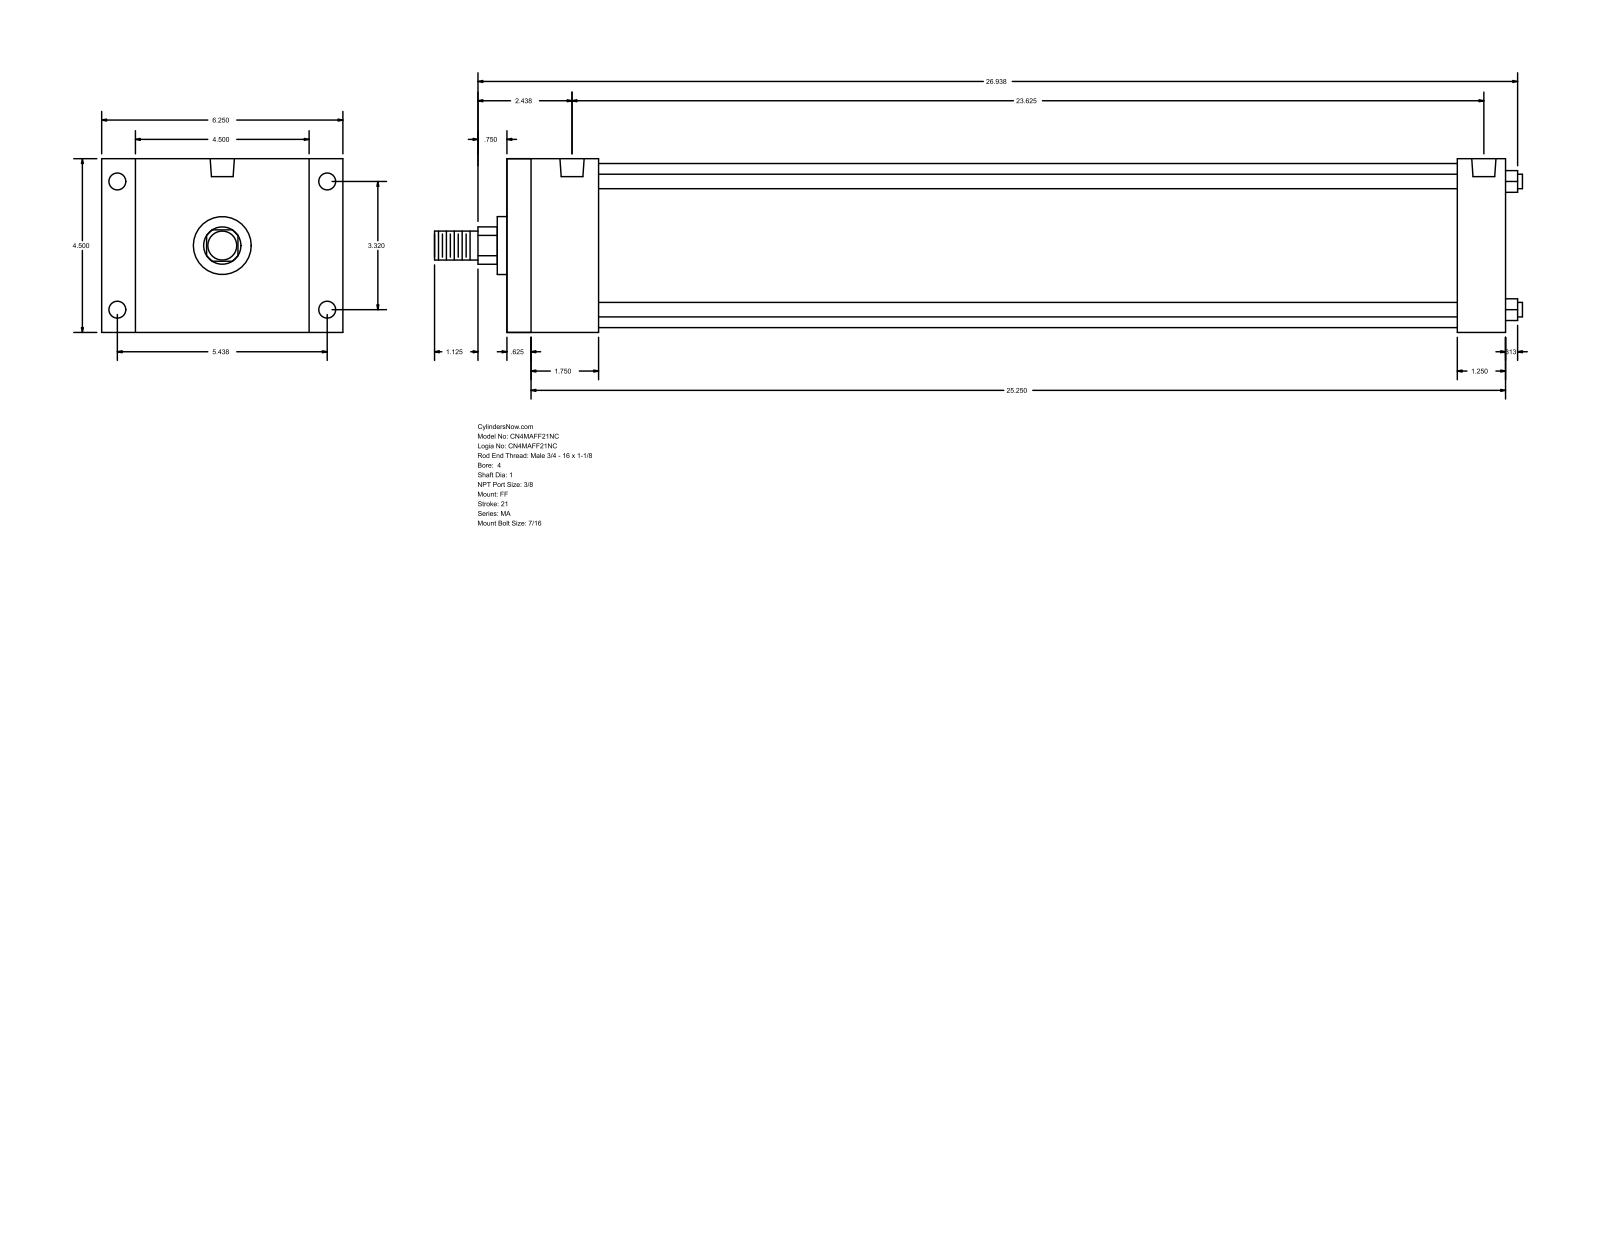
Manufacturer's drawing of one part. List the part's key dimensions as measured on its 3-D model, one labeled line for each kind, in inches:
Part name (STEP PRODUCT): MA_FF__0400_1
STEP written by: GSSL Pune (CONFIG_CONTROL_DESIGN)
Units: inches
Bodies: 0 solids, 92 faces (64 planar, 28 cylindrical, 0 other)
Overall size (bounding box): 28.187 × 6.25 × 4.5
Round holes (diameter × count): ⌀0.437 ×8, ⌀0.627 ×2
Round bosses / shafts (diameter × count): ⌀0.375 ×4, ⌀4.25 ×1, ⌀1.5 ×1, ⌀1 ×1, ⌀0.75 ×1
Partial cylindrical surfaces — rounded edges, fillets, slot ends (radius × count): R0.484 ×1
Main face-to-face distances: 4.5, 25.875, 0.625, 25.25, 0.875, 5.375, 24.625, 24, 1.25, 2.375
Hole centre spacings: 0.187, 3.32, 5.438, 6.371, 23.25, 23.438, 23.625
